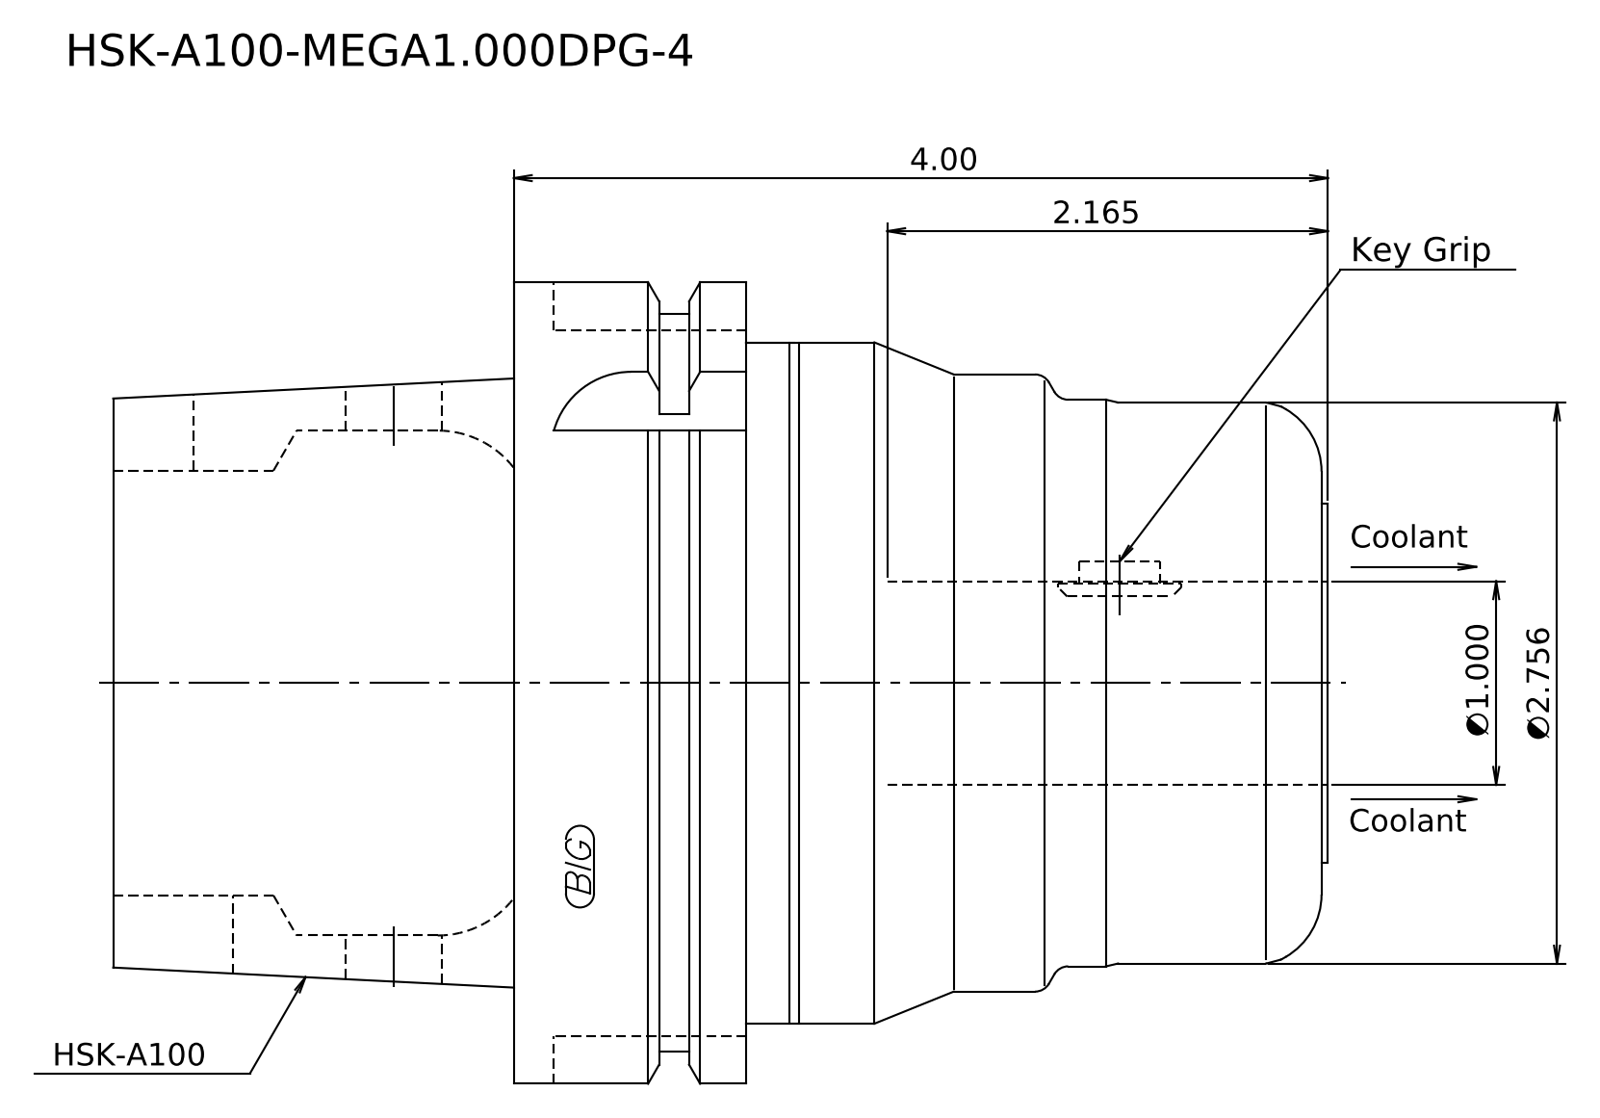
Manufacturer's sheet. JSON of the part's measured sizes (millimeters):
{"step_written_by": "Kubotek KeyCreator 2011 V10.0.2 (22737) (automotive_design)", "units": "millimeters", "bodies": {"solids": 1, "faces": 23, "planar": 7, "cylindrical": 8, "other": 8}, "overall_size": [151.6, 100, 100], "volume_mm3": 762299, "surface_area_mm2": 52844, "round_bosses_or_shafts": [[100, 1], [92, 1], [85, 1], [77, 1], [70.7, 1], [70, 1], [44.8, 1]], "face_to_face_distances": [50, 29, 79, 72.6, 101.6, 151.6, 0.8, 71.8, 100.8, 150.8]}
